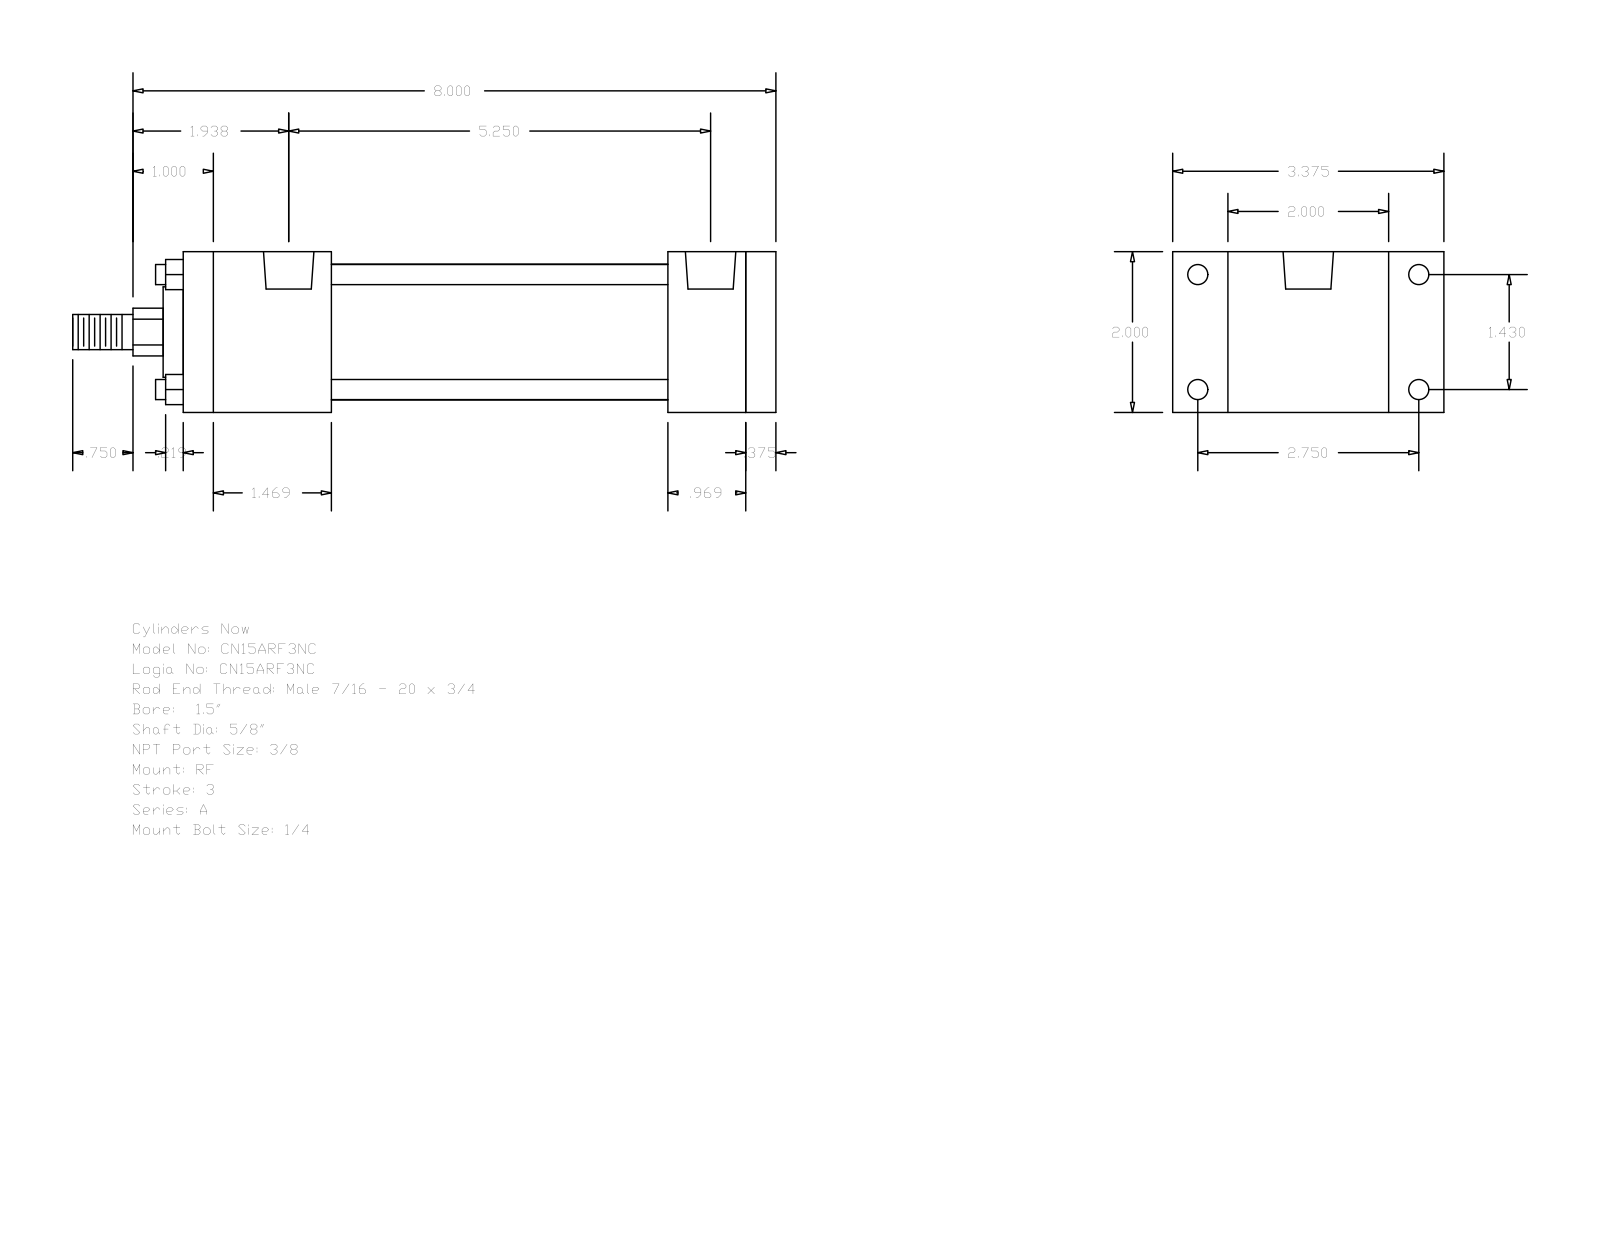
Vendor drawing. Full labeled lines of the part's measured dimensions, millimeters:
Part name (STEP PRODUCT): A_RF__0150_0.625
STEP written by: GSSL Pune (CONFIG_CONTROL_DESIGN)
Units: millimetres
Bodies: 0 solids, 92 faces (64 planar, 28 cylindrical, 0 other)
Overall size (bounding box): 222.25 × 85.72 × 50.8
Round holes (diameter × count): ⌀5.56 ×4, ⌀6.35 ×4, ⌀15.93 ×2
Round bosses / shafts (diameter × count): ⌀6.35 ×4, ⌀42.93 ×1, ⌀28.57 ×1, ⌀15.88 ×1, ⌀11.11 ×1
Partial cylindrical surfaces — rounded edges, fillets, slot ends (radius × count): R7.54 ×1
Main face-to-face distances: 50.8, 9.52, 177.8, 187.32, 153.19, 24.61, 34.13, 46.83, 106.36, 130.97
Hole centre spacings: 3.97, 36.32, 69.84, 78.72, 125.41, 129.38, 133.35
